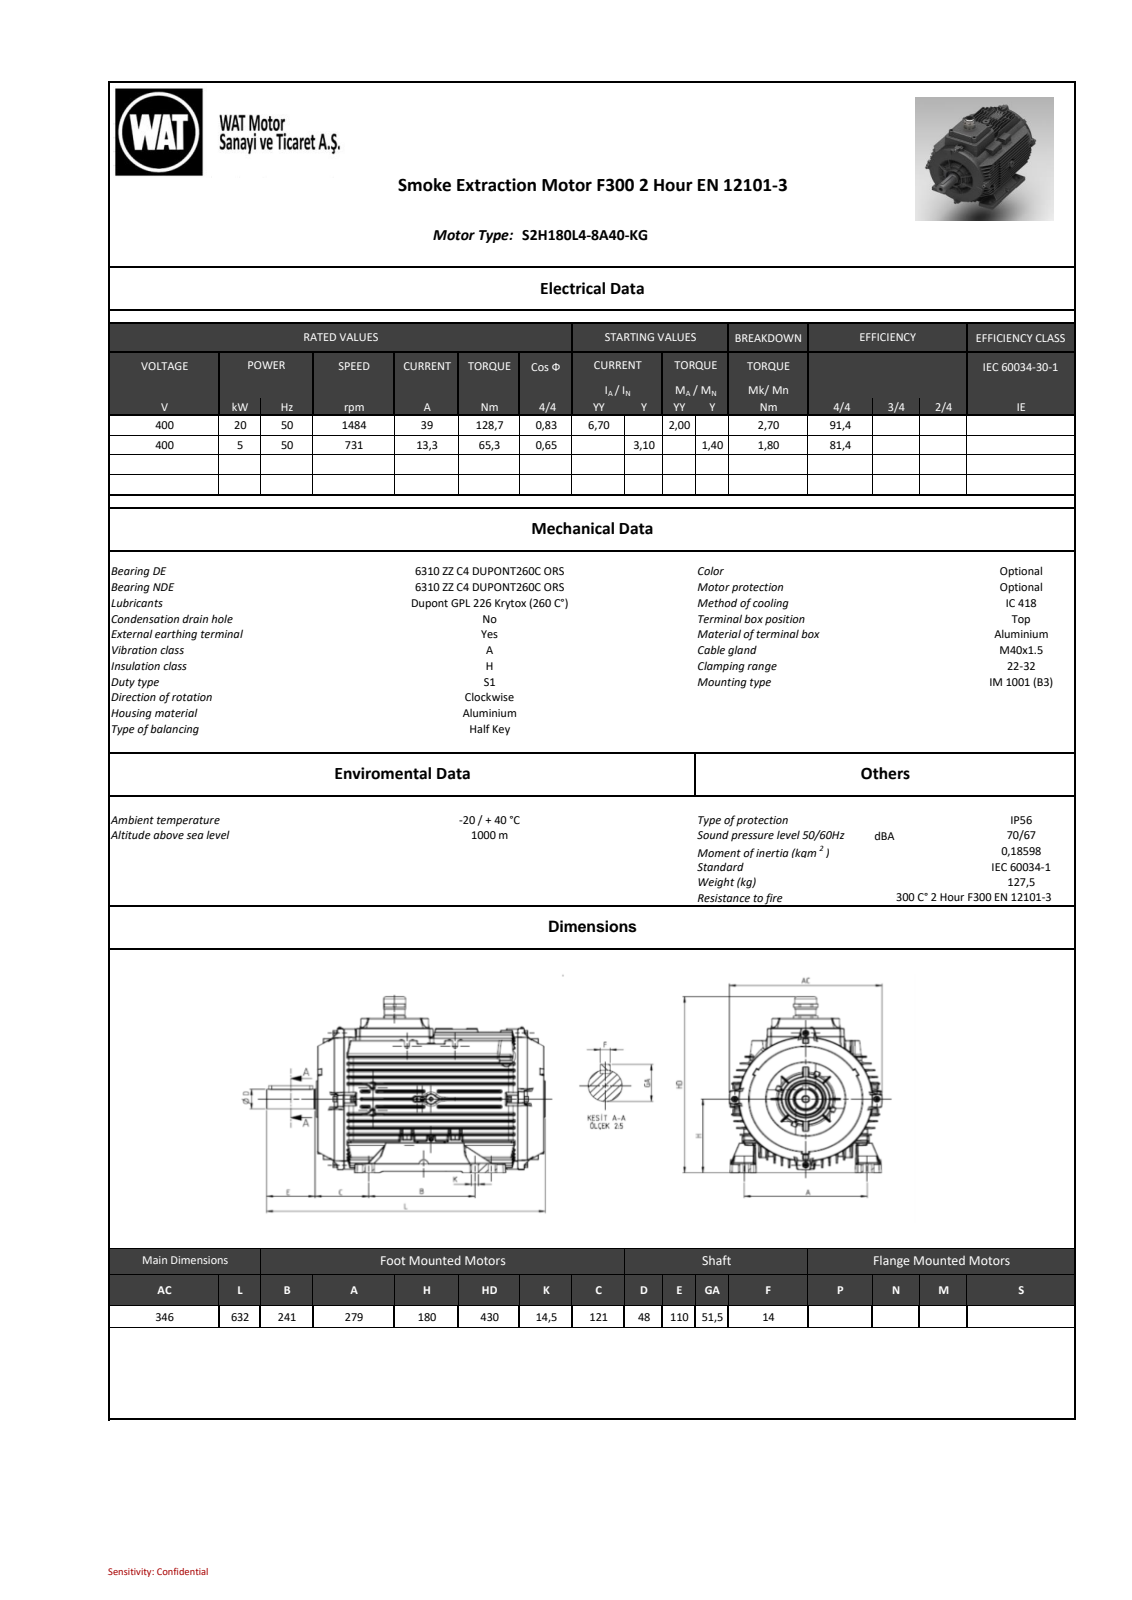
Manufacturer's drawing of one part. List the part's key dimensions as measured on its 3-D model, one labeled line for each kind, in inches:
Part name (STEP PRODUCT): 001_objects
STEP written by: SIEMENS PLM Software NX2206.8101 (AP203_CONFIGURATION_CONTROLLED_3D_DESIGN_OF_MECHANICAL_PARTS_AND_ASSEMBLIES_MIM_LF)
Units: inches
Bodies: 0 solids, 6807 faces (1319 planar, 2205 cylindrical, 3283 other)
Overall size (bounding box): 24.882 × 16.969 × 13.622
Round holes (diameter × count): ⌀0.551 ×1, ⌀0.669 ×1, ⌀1.26 ×1, ⌀2.441 ×1, ⌀2.984 ×1, ⌀2.992 ×1, ⌀3.15 ×1
Round bosses / shafts (diameter × count): ⌀0.583 ×4, ⌀0.501 ×4, ⌀0.472 ×4, ⌀0.315 ×4, ⌀0.787 ×2, ⌀0.272 ×2, ⌀11.929 ×1, ⌀1.969 ×1
Partial cylindrical surfaces — rounded edges, fillets, slot ends (radius × count): R0.079 ×642, R0.039 ×525, R0.02 ×122, R0.197 ×64, R0.059 ×29, R0.03 ×20, R0.031 ×12, R0.004 ×9
Main face-to-face distances: 0.638, 1.279, 0.641, 6.734, 6.844, 5.565, 6.206, 6.184, 5.546, 4.905
